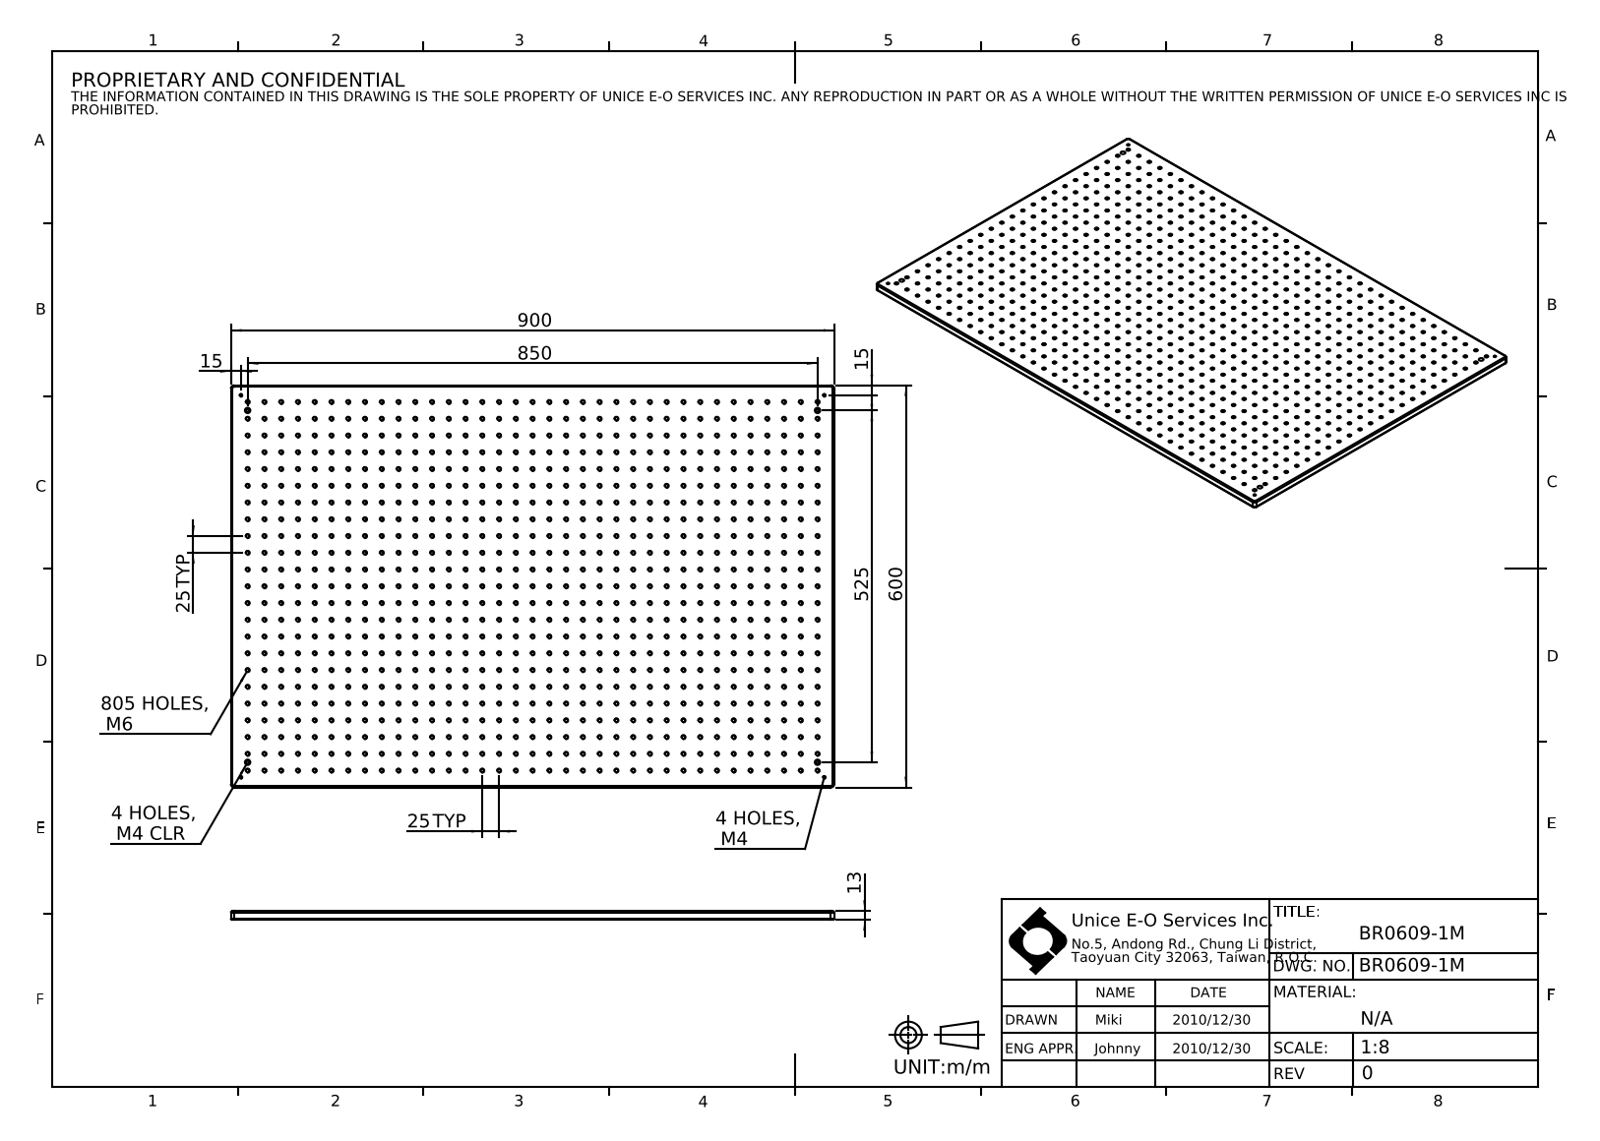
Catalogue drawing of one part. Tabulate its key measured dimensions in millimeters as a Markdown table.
| quantity | value |
| --- | --- |
| part name | BR0609-1M |
| STEP written by | SolidWorks 2016 (CONFIG_CONTROL_DESIGN) |
| units | millimeters |
| bodies | 1 solid, 1664 faces (10 planar, 1646 cylindrical, 8 other) |
| overall size | 900 × 600 × 13 |
| volume | 6 807 000 mm³ |
| surface area | 1 248 000 mm² |
| round holes (diameter × count) | 5 × 805, 3.3 × 4, 4.5 × 4, 8 × 4 |
| partial cylindrical surfaces (radius × count) | 2 × 8, 5 × 4 |
| main face-to-face distances | 13, 600, 900, 7, 6 |
| hole center spacings | 25, 50, 75, 100, 125, 150, 175, 200 |
